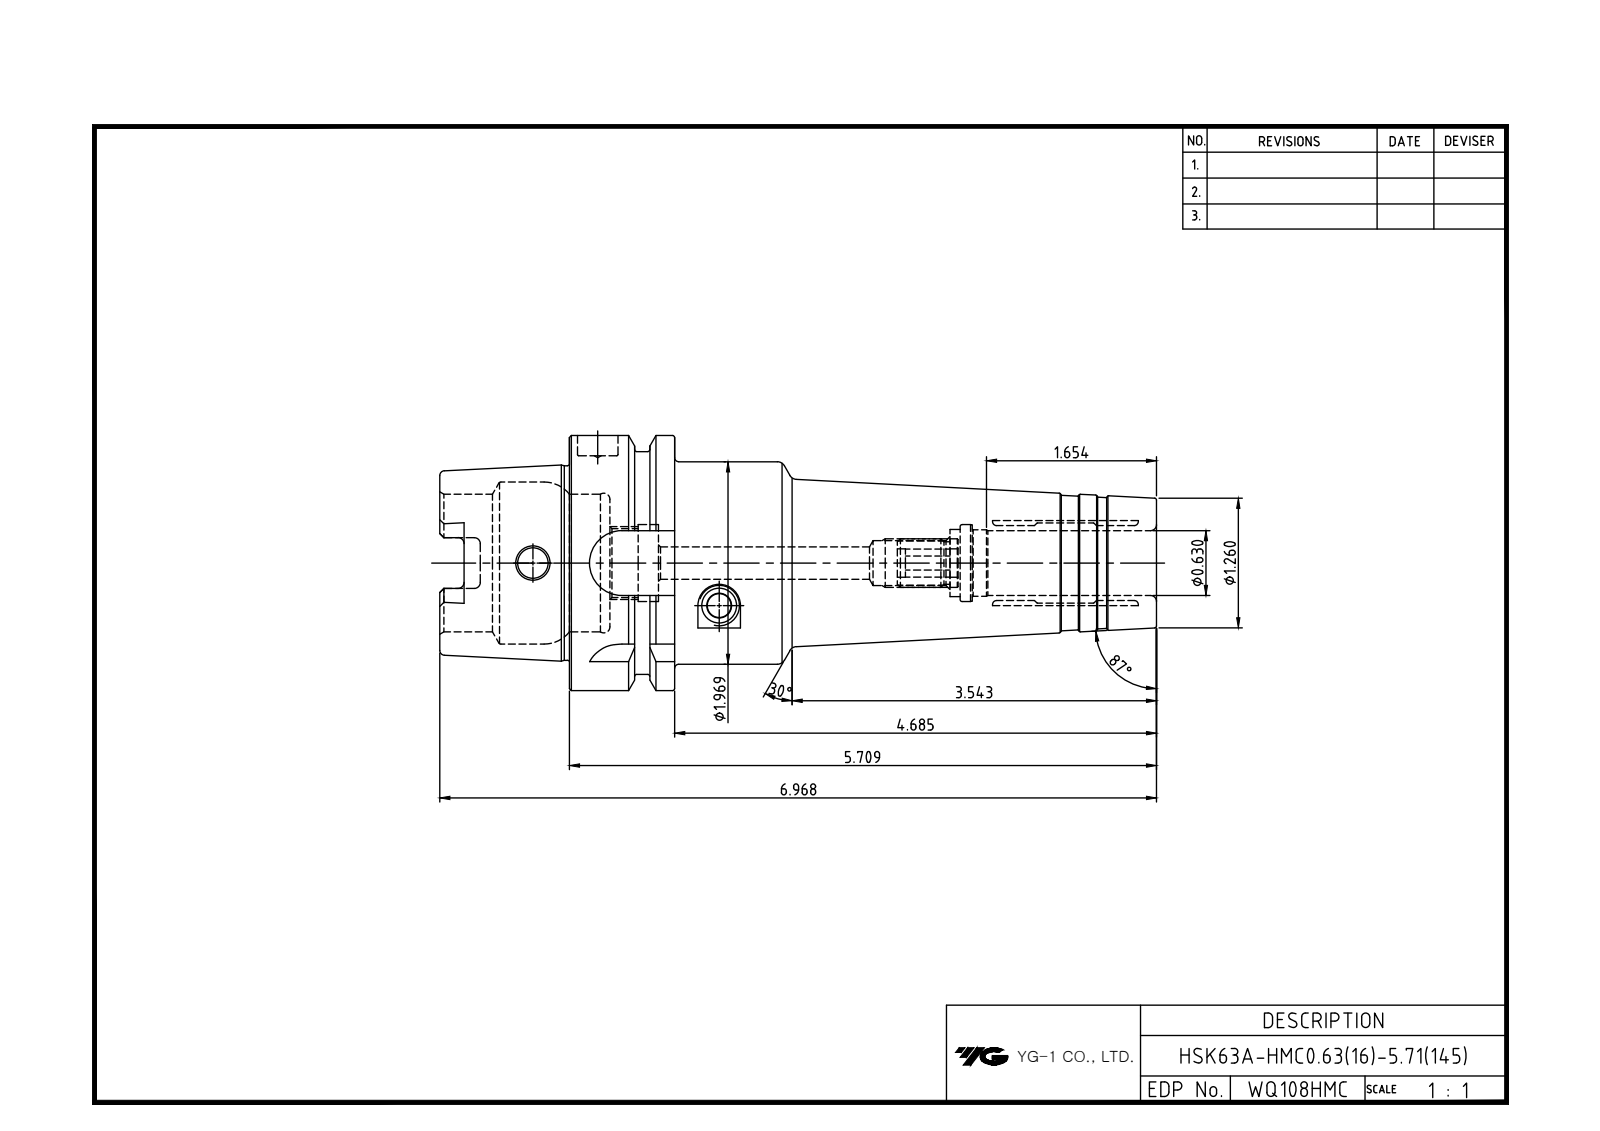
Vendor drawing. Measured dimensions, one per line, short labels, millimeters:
name: LO-HSK63A-HMC16-145
written by: Autodesk Inventor 2020 (AUTOMOTIVE_DESIGN)
unit: mm
bodies: 1 solid, 136 faces (42 planar, 34 cylindrical, 60 other)
size: 177 × 63 × 63
volume: 218 603 mm³; area: 40 772 mm²
holes: 1× ⌀7.5, 1× ⌀8, 1× ⌀10, 1× ⌀10.92, 1× ⌀16, 1× ⌀16.6, 1× ⌀16.92, 1× ⌀19, 1× ⌀34, 1× ⌀40
bosses: 1× ⌀63, 1× ⌀55, 1× ⌀50, 1× ⌀48.04
rounds: 6× R1.5, 4× R2.88, 4× R8
face distances: 26, 10, 16, 119, 145, 135, 32, 42, 58, 177
